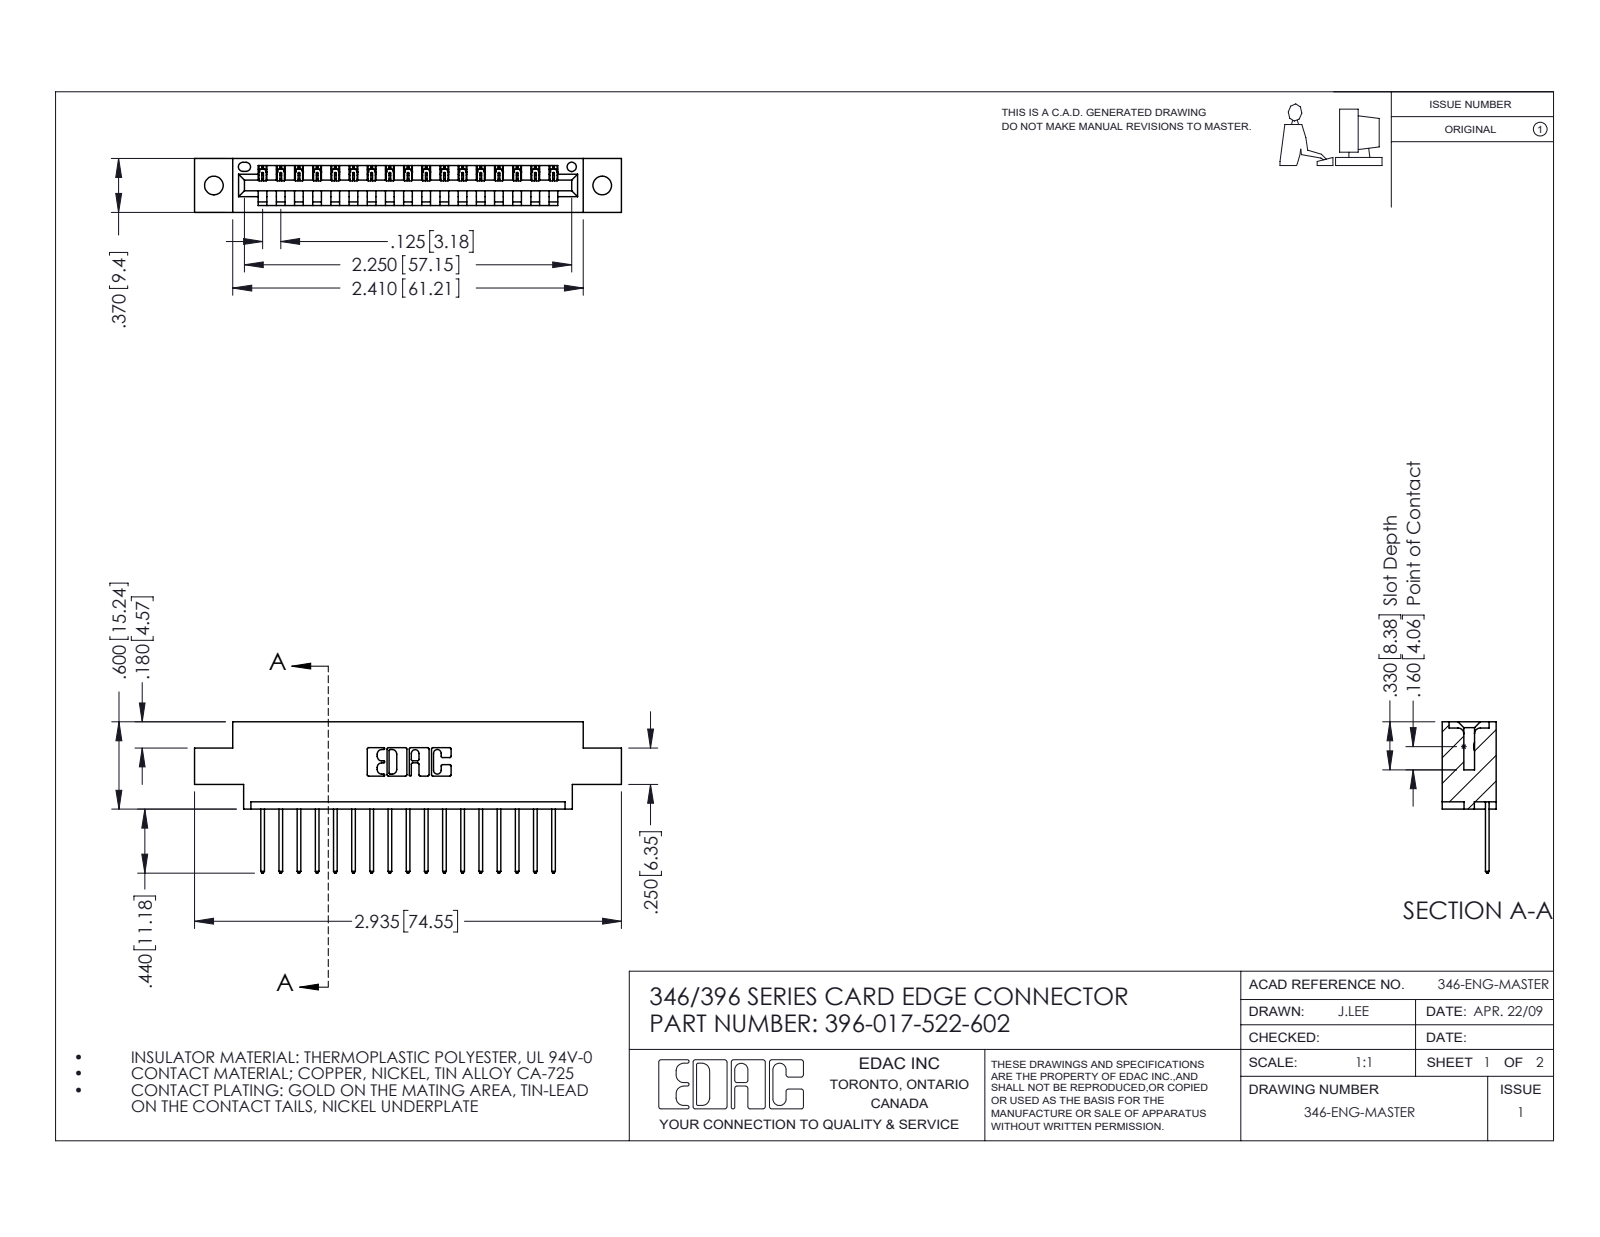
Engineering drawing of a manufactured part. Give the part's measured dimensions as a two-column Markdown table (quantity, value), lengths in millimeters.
| quantity | value |
| --- | --- |
| part name | 345-292-001_345-293-122; 346 Part_0.170 Offset - 0.128 Dia; 396-017-522-602 |
| STEP written by | SolidWorks 2016 (CONFIG_CONTROL_DESIGN) |
| units | millimeters |
| bodies | 18 solids, 1112 faces (760 planar, 352 cylindrical, 0 other) |
| overall size | 74.5 × 26.4 × 9.4 |
| volume | 6 770 mm³ |
| surface area | 8 148 mm² |
| round holes (diameter × count) | 3.3 × 2, 1.6 × 1 |
| partial cylindrical surfaces (radius × count) | 0.2 × 34, 0.3 × 34, 0.3 × 22, 0.2 × 6, 0.8 × 6, 0.7 × 3, 0.8 × 2, 1 × 2 |
| main face-to-face distances | 1.2, 8.2, 9.4, 6.4, 1.8, 7.6, 0.6, 3.8, 5.6, 2.5 |
| hole center spacings | 6.2, 62.6, 67.8 |
